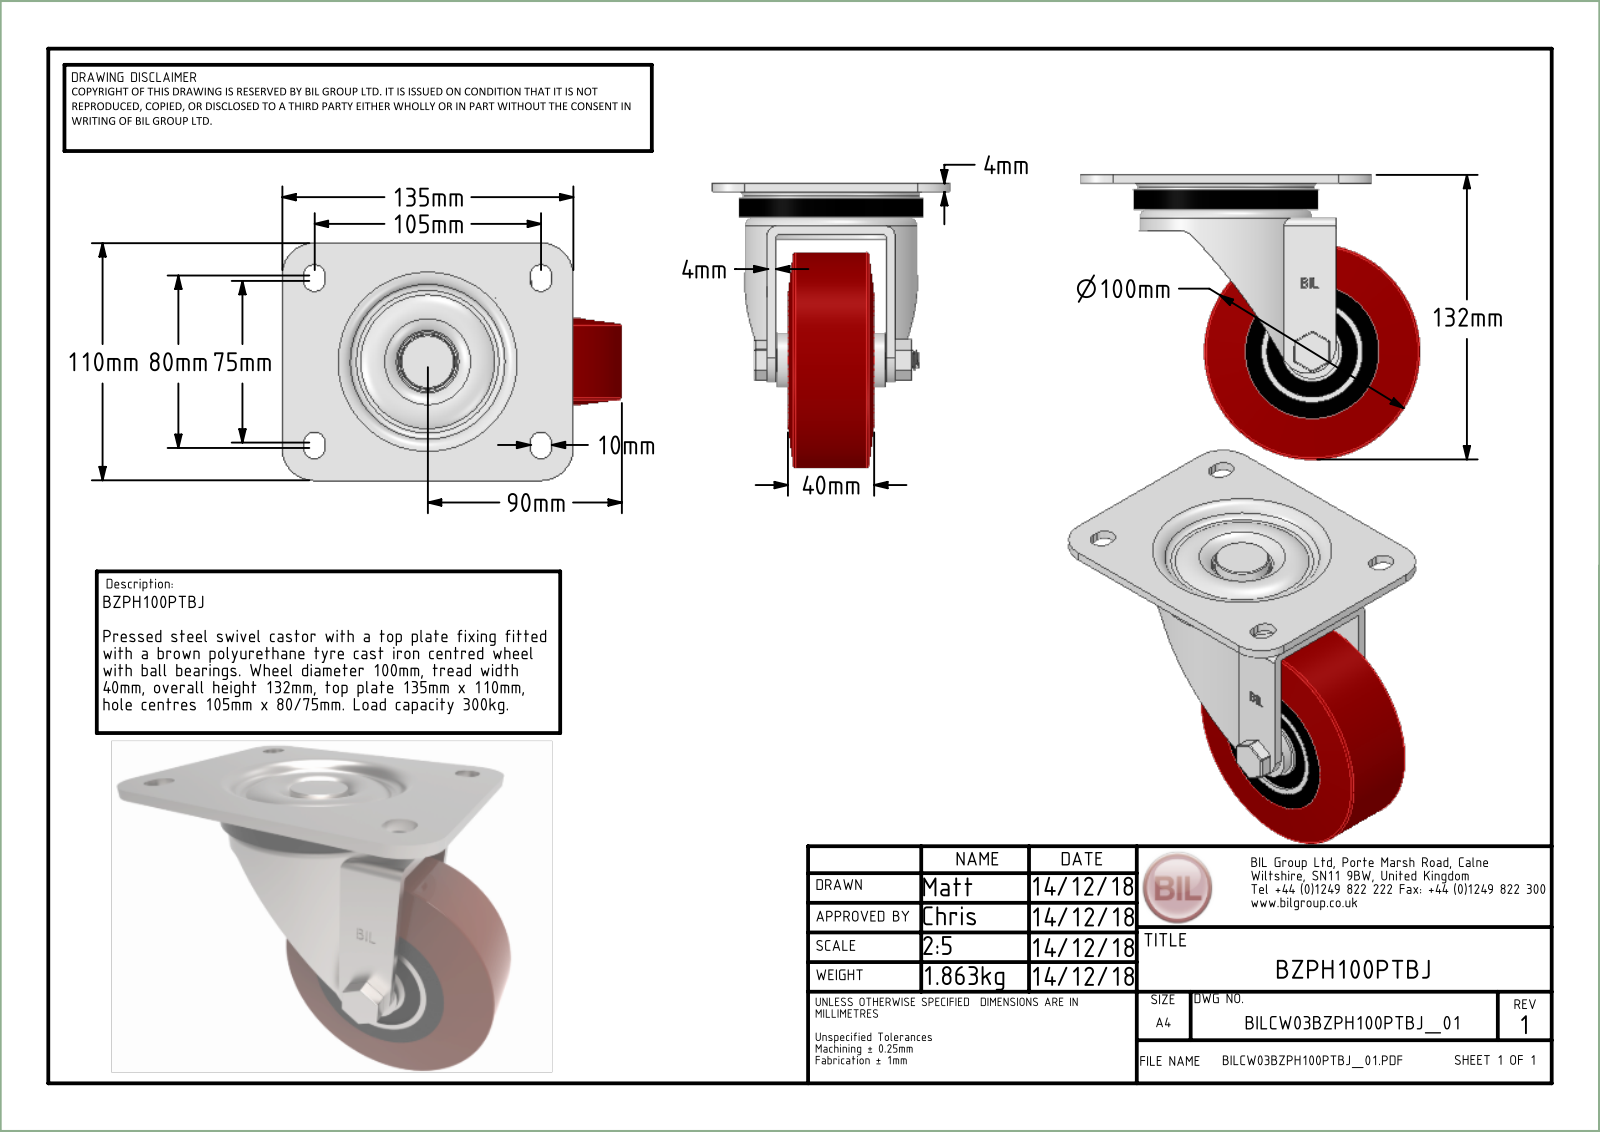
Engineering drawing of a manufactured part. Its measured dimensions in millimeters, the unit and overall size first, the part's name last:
Units: millimetres
Overall size (bounding box): 157.5 × 132 × 110
Round holes (diameter × count): ⌀10 ×1, ⌀10.2 ×1, ⌀10.5 ×1, ⌀12 ×1, ⌀20 ×1, ⌀26 ×1, ⌀28 ×1, ⌀28.5 ×1, ⌀30 ×1, ⌀41.5 ×1, ⌀42 ×1, ⌀44 ×1
Round bosses / shafts (diameter × count): ⌀25 ×2, ⌀100 ×1, ⌀83.5 ×1, ⌀80 ×1, ⌀51 ×1, ⌀40.5 ×1, ⌀40 ×1, ⌀32 ×1
Partial cylindrical surfaces — rounded edges, fillets, slot ends (radius × count): R0.5 ×18, R4 ×14, R6 ×12, R5.5 ×8, R0.75 ×6, R2 ×4, R15 ×4, R13.6 ×1
Main face-to-face distances: 4, 13, 9, 40, 26, 35.5, 55, 13.5, 19.5, 5.5
Volume: 448 139 mm³ · Surface area: 166 391 mm²
Bodies: 38 solids, 1348 faces (643 planar, 268 cylindrical, 437 other)
Part name (STEP PRODUCT): BZPH100PTBJ v2; BZPH100AS v1; ZINC PLATED, PRESSED STEEL TOP PLATE; ZINC PLATED, PRESSED STEEL FORKS (+8 more)
STEP written by: Autodesk Translation Framework v14.10.0.0 (AUTOMOTIVE_DESIGN)
